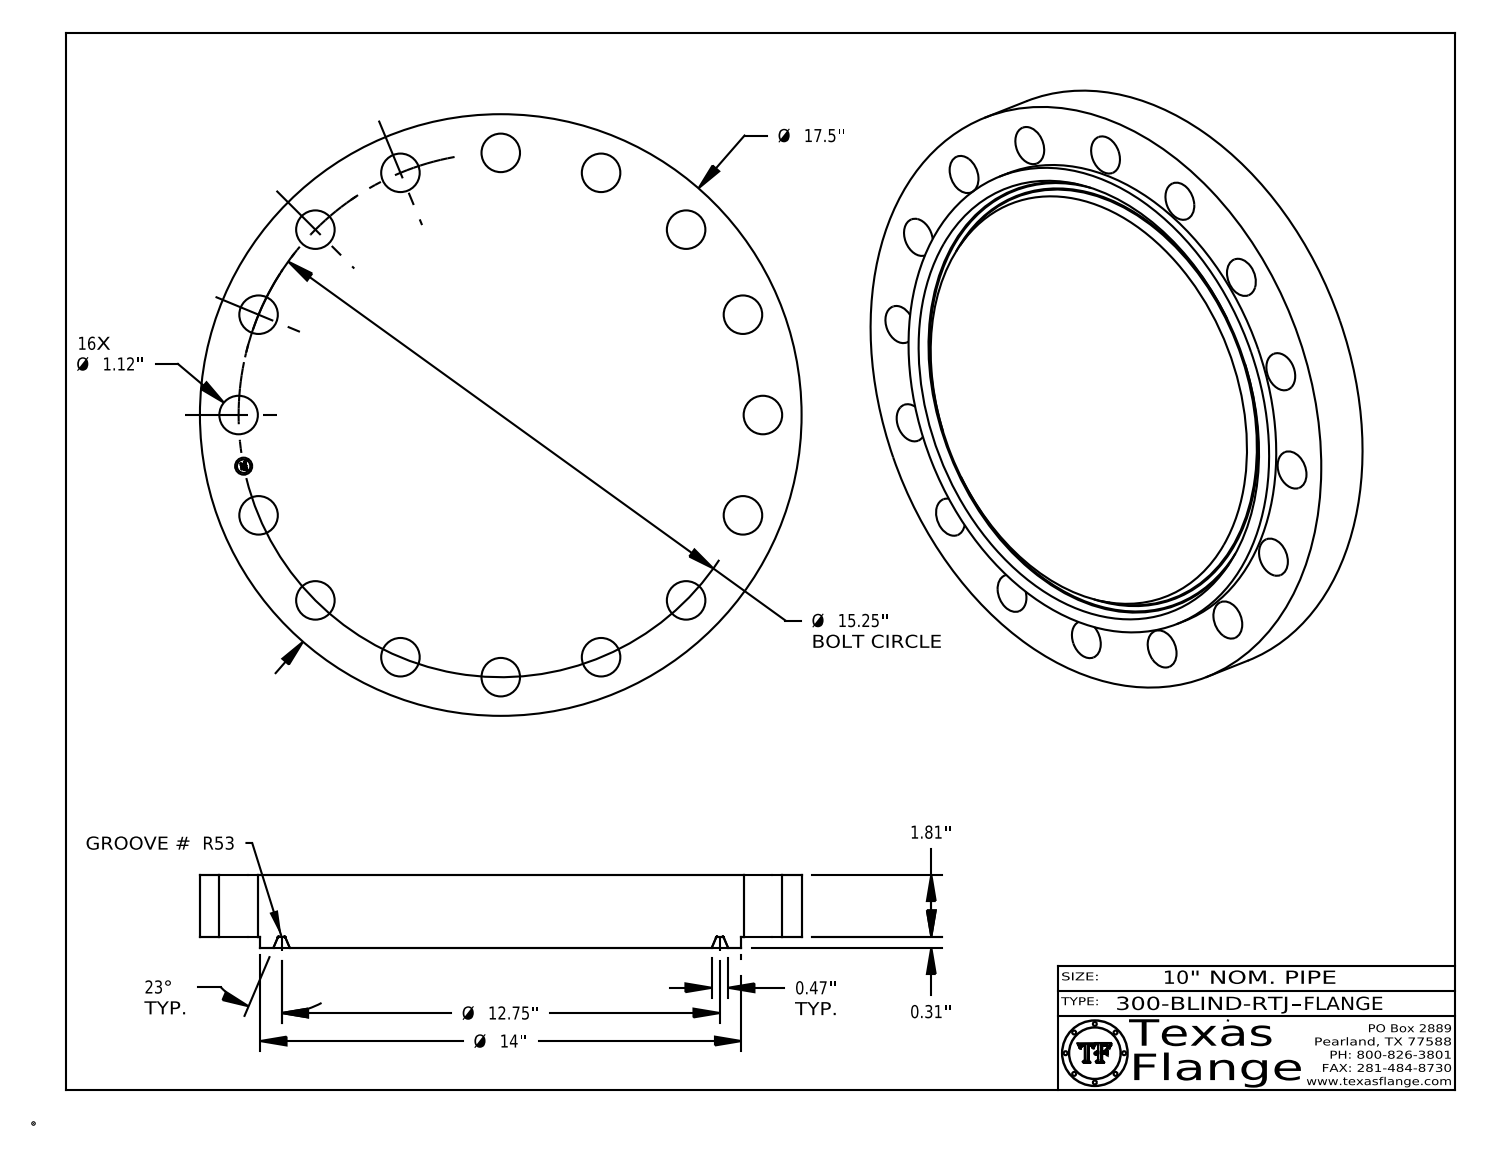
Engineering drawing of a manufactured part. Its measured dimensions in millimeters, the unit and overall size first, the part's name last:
Units: millimetres
Overall size (bounding box): 444.5 × 444.5 × 53.9
Round holes (diameter × count): ⌀28.4 ×16, ⌀12.6 ×1
Round bosses / shafts (diameter × count): ⌀0.8 ×8, ⌀444.5 ×1, ⌀355.6 ×1, ⌀9.9 ×1
Main face-to-face distances: 53.9, 8, 46, 0.4, 53.5, 45.6, 3.8, 3.7, 0.7, 2.4
Hole centre spacings: 215.2, 273.9, 379.9, 357.9, 75.6, 75.6, 148.2, 322.1
Volume: 7 386 000 mm³ · Surface area: 439 400 mm²
Bodies: 1 solid, 434 faces (370 planar, 56 cylindrical, 8 other)
Part name (STEP PRODUCT): 300-BLIND-RTJ
STEP written by: CATIA V5 STEP AP214 (AUTOMOTIVE_DESIGN)
